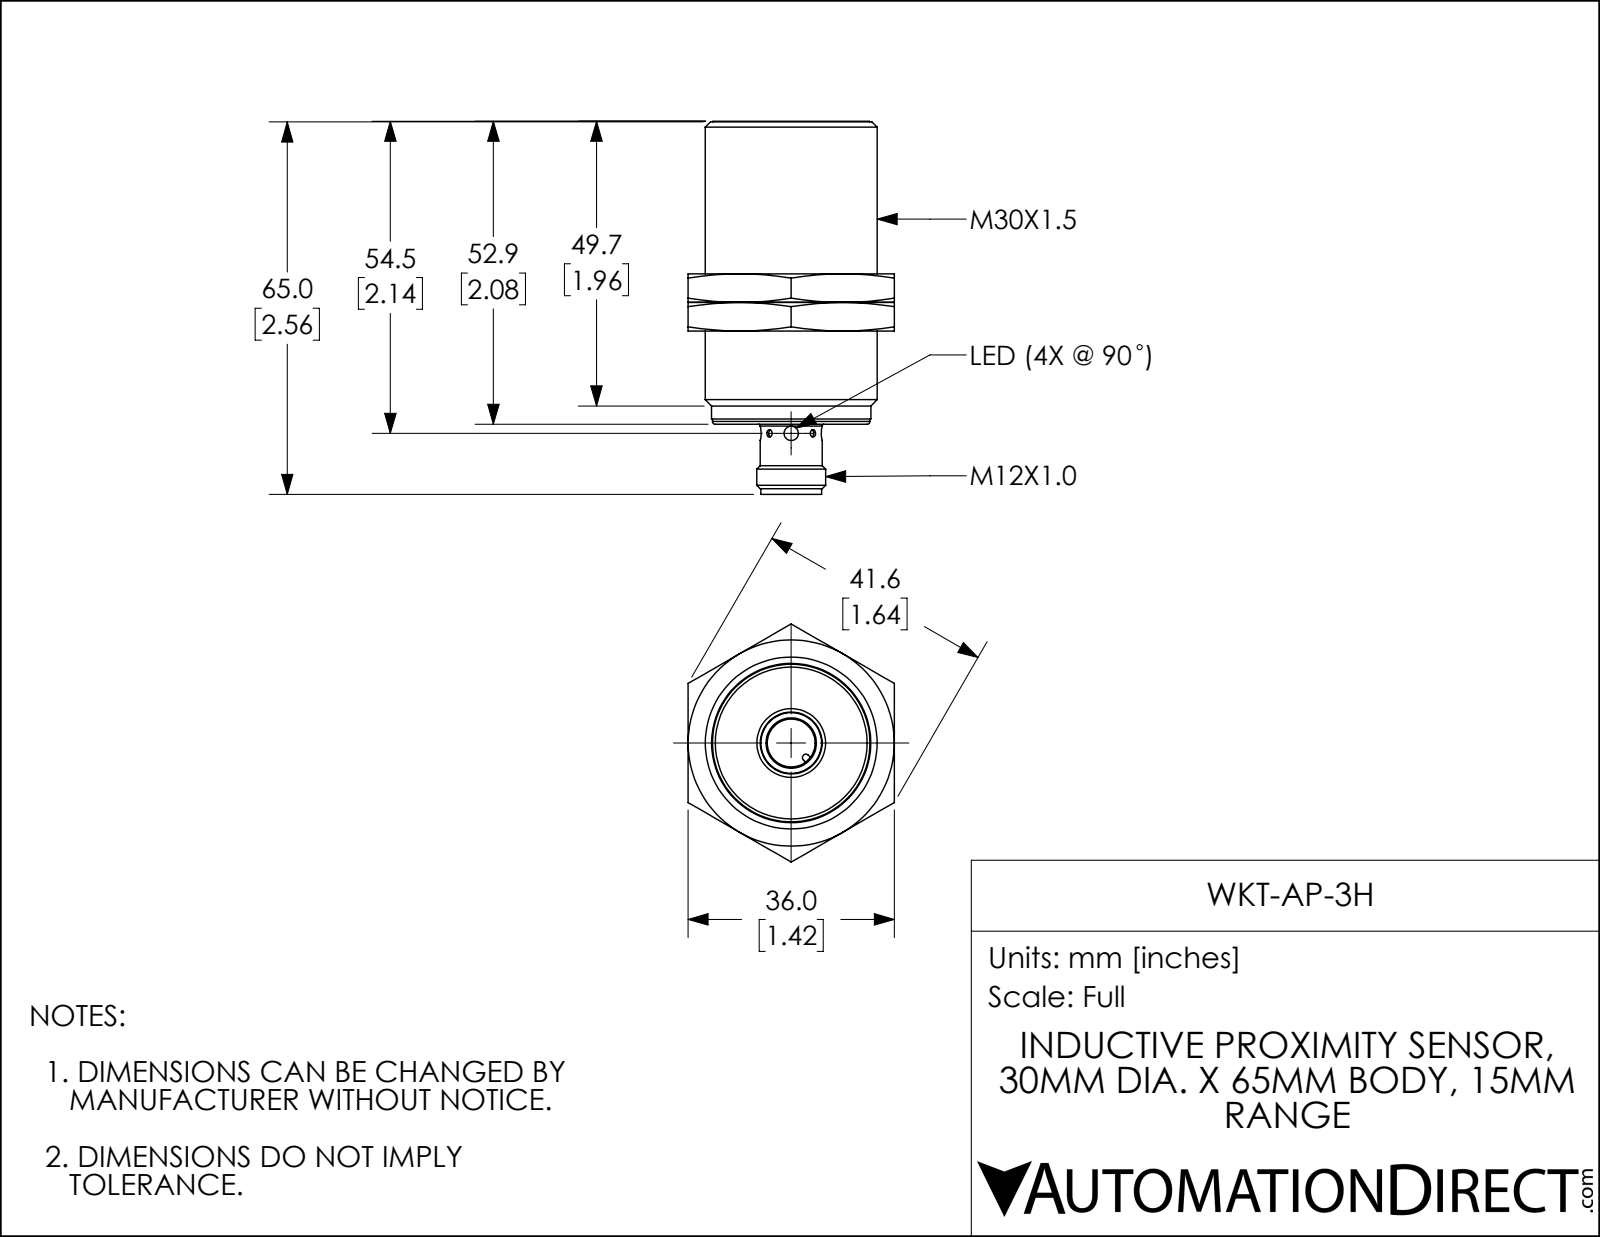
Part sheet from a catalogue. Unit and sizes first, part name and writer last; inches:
Units: inches
Overall size (bounding box): 2.563 × 1.637 × 1.417
Round holes (diameter × count): ⌀0.051 ×2, ⌀0.098 ×2, ⌀0.329 ×1, ⌀1.117 ×1
Round bosses / shafts (diameter × count): ⌀1.181 ×1, ⌀1.094 ×1, ⌀1.083 ×1, ⌀1.076 ×1, ⌀0.472 ×1, ⌀0.425 ×1, ⌀0.417 ×1
Partial cylindrical surfaces — rounded edges, fillets, slot ends (radius × count): R0.024 ×1, R0.195 ×1
Main face-to-face distances: 0.197, 1.244, 1.417, 0.837, 2.082, 0.641, 1.441, 1.034, 0.394, 1.048
Volume: 2.583 in³ · Surface area: 16.69 in²
Bodies: 3 solids, 88 faces (26 planar, 27 cylindrical, 35 other)
Part name (STEP PRODUCT): WKT-AP-3H
STEP written by: SolidWorks 2017 (AUTOMOTIVE_DESIGN)
